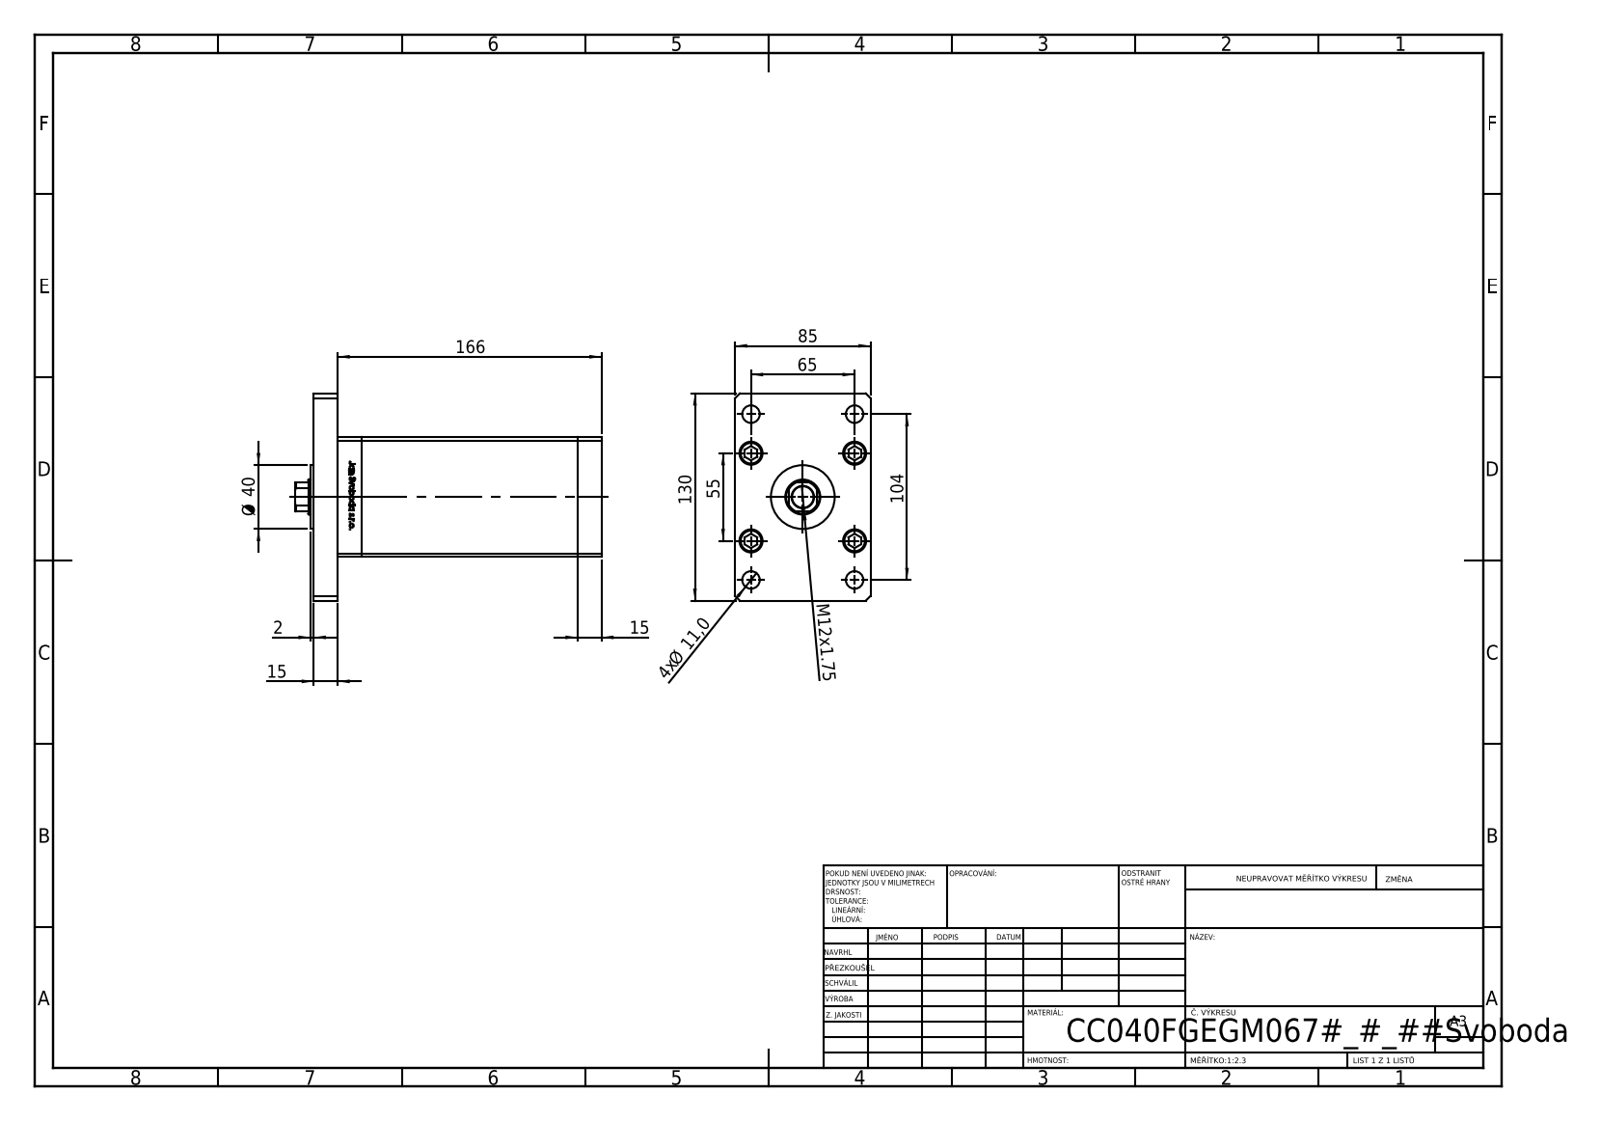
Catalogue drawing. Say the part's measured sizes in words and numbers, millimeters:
The part is named "V220C_VC_F; V220C_F; V220C_FRONT_F; V220C BACK_F (+2 more)". Its 3-D file was written by "SolidWorks 2019 (CONFIG_CONTROL_DESIGN)". It is 19 solids with 1310 faces: 517 planar, 187 cylindrical and 606 other. Overall it measures 192 by 130 by 85 millimeters. Its volume is 1 096 000 cubic millimeters and its surface area 191 941 square millimeters. Round holes: 9 of diameter 11, 5 of diameter 15.5, 4 of diameter 10, 4 of diameter 14.5, 2 of diameter 2, 2 of diameter 13.16, 1 of diameter 13.5, 1 of diameter 22, 1 of diameter 23.5. Round bosses or shafts: 9 of diameter 8, 5 of diameter 14.5, 1 of diameter 40. Partial cylindrical surfaces (rounded edges, fillets, slot ends): 2 of radius 0.93, 1 of radius 10.5. The main face-to-face distances are 15, 150.5, 165.5, 85, 75, 30, 135.5, 180.5, 27.5, 10.5. The hole center spacings are 28, 24.5, 42.57, 61.32, 65, 69.46, 79.5, 102.69.
